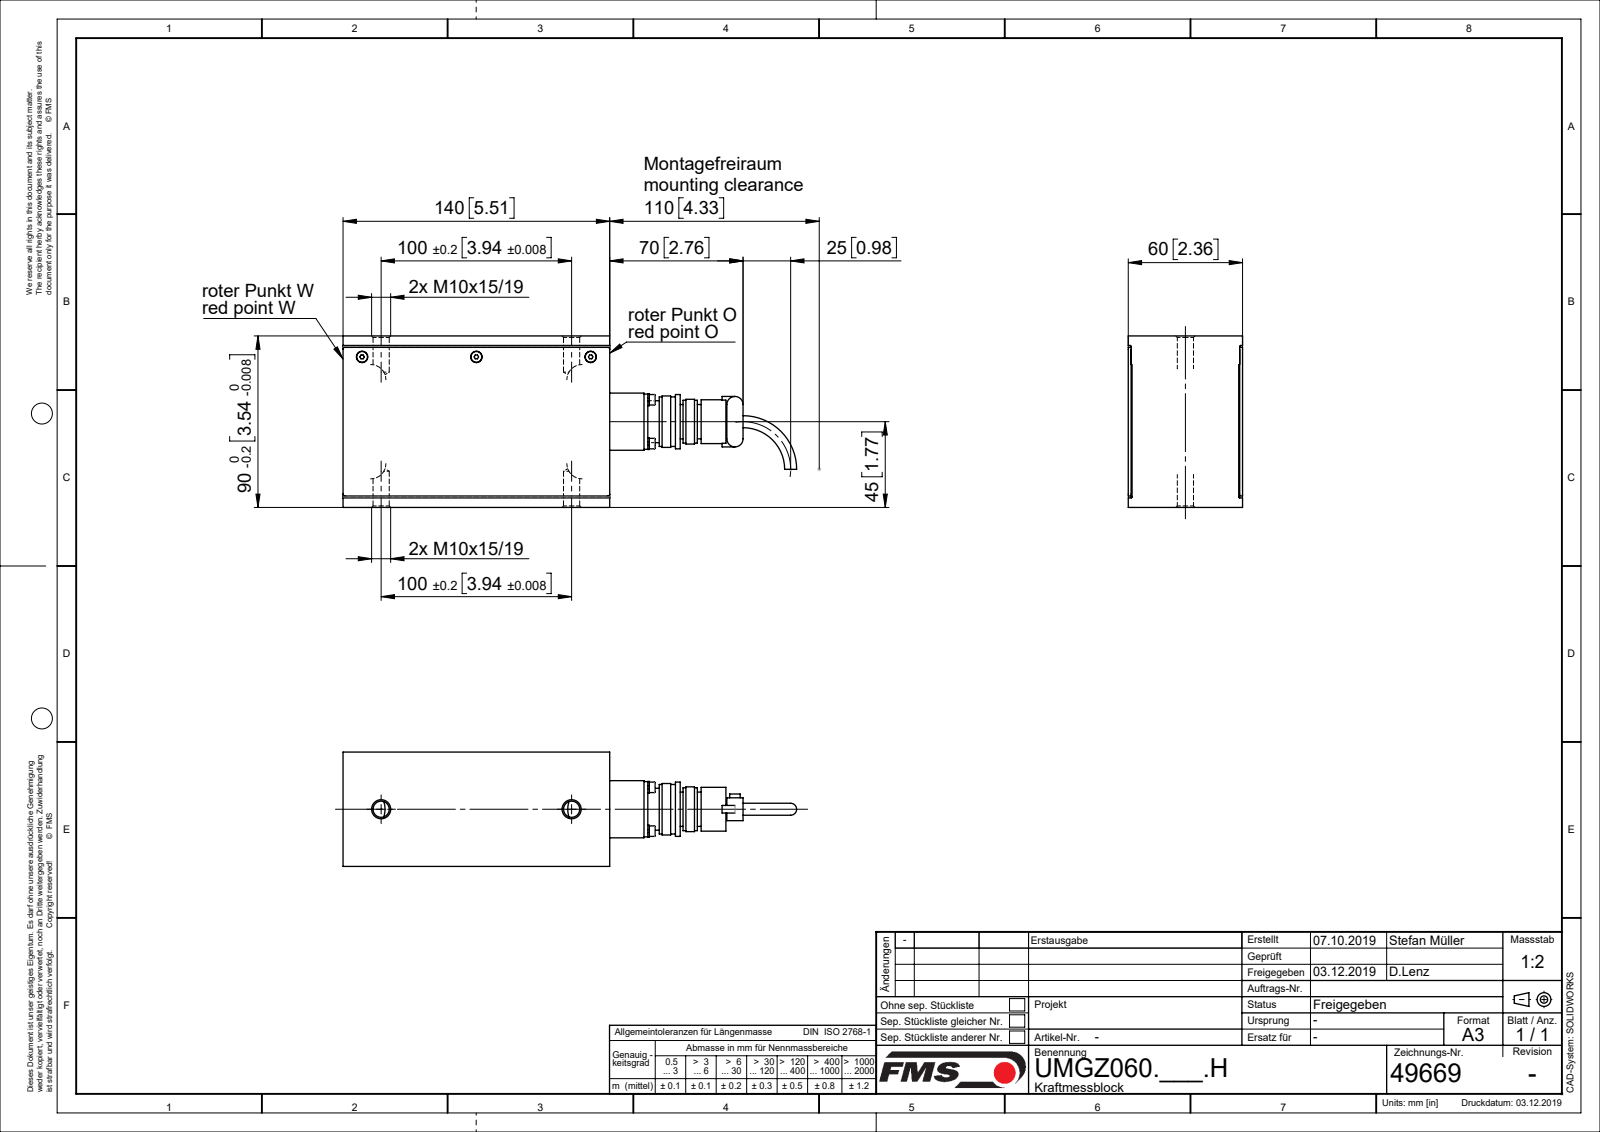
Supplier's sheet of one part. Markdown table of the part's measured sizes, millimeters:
| quantity | value |
| --- | --- |
| part name | U49669; U4945304; U49515; KABELDOSE_PG_AMPH_4-POL (+4 more) |
| STEP written by | Mechanical Desktop 2007 (CONFIG_CONTROL_DESIGN) |
| units | millimeters |
| bodies | 18 solids, 366 faces (128 planar, 152 cylindrical, 86 other) |
| overall size | 242.5 × 95 × 60 |
| volume | 770 026 mm³ |
| surface area | 113 266 mm² |
| round holes (diameter × count) | 2.6 × 7, 3.2 × 4, 6 × 3, 8.68 × 2 |
| round bosses / shafts (diameter × count) | 3 × 7, 6.2 × 4, 5.5 × 4, 2.5 × 4, 28 × 1, 23 × 1, 22 × 1, 21 × 1 |
| partial cylindrical surfaces (radius × count) | 1 × 4, 4 × 4 |
| main face-to-face distances | 1.5, 58.5, 2, 58, 0.5, 56.5, 57, 60, 56, 90 |
| hole center spacings | 23, 32.53, 60, 100, 120 |
